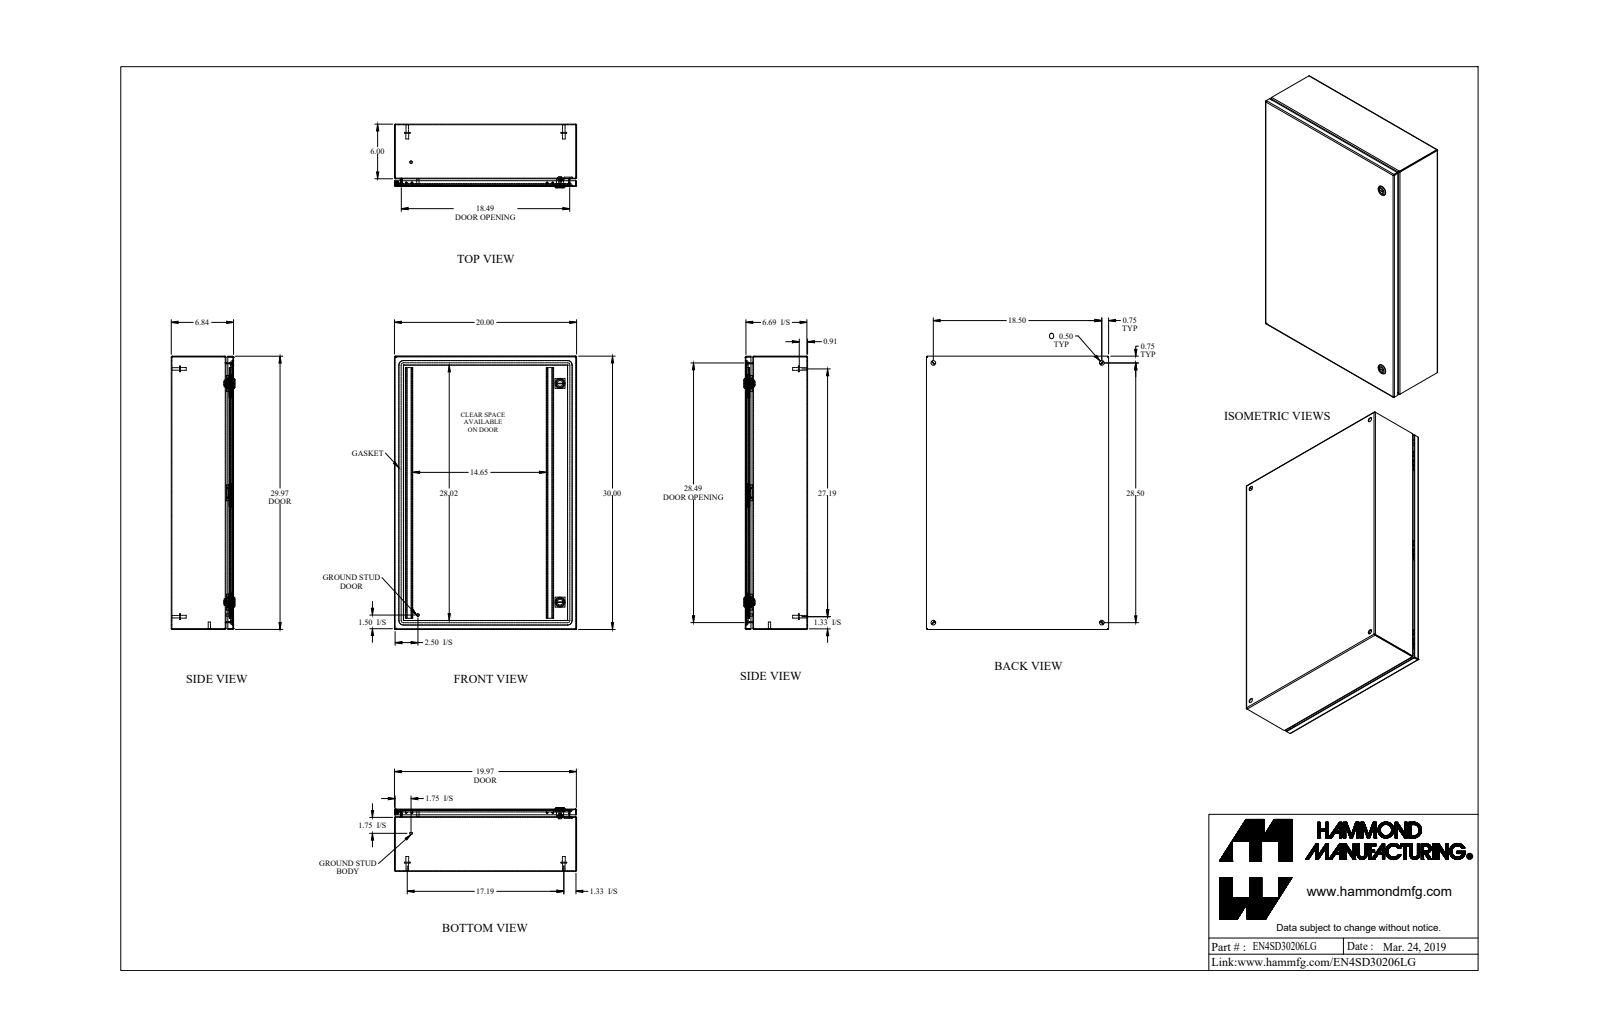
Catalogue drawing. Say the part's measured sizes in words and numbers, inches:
The part is named "EN4SD30206LG_Default". Its 3-D file was written by "SolidWorks 2019 (CONFIG_CONTROL_DESIGN)". It is 31 solids with 885 faces: 422 planar, 295 cylindrical and 168 other. Overall it measures 30 by 20 by 6.997 inches. Its volume is 157.4 cubic inches and its surface area 4 430 square inches. Round holes: 4 of diameter 0.5, 2 of diameter 0.232, 2 of diameter 0.625, 2 of diameter 0.785, 1 of diameter 0.172, 1 of diameter 0.24, 1 of diameter 0.242. Round bosses or shafts: 4 of diameter 0.625, 4 of diameter 0.313, 4 of diameter 0.27, 2 of diameter 1.1, 2 of diameter 0.525, 2 of diameter 0.281, 2 of diameter 0.25, 1 of diameter 0.455. Partial cylindrical surfaces (rounded edges, fillets, slot ends): 20 of radius 0.036, 20 of radius 0.108, 12 of radius 0.043, 12 of radius 0.081, 12 of radius 0.382, 8 of radius 19.003, 6 of radius 0.006, 6 of radius 0.062. The main face-to-face distances are 0.072, 6.765, 6.693, 6.837, 19.928, 29.928, 19.856, 20, 0.837, 5.928. The hole center spacings are 18.5, 28.5, 33.978, 2.493, 2.494, 17.572, 17.572, 23.999.
